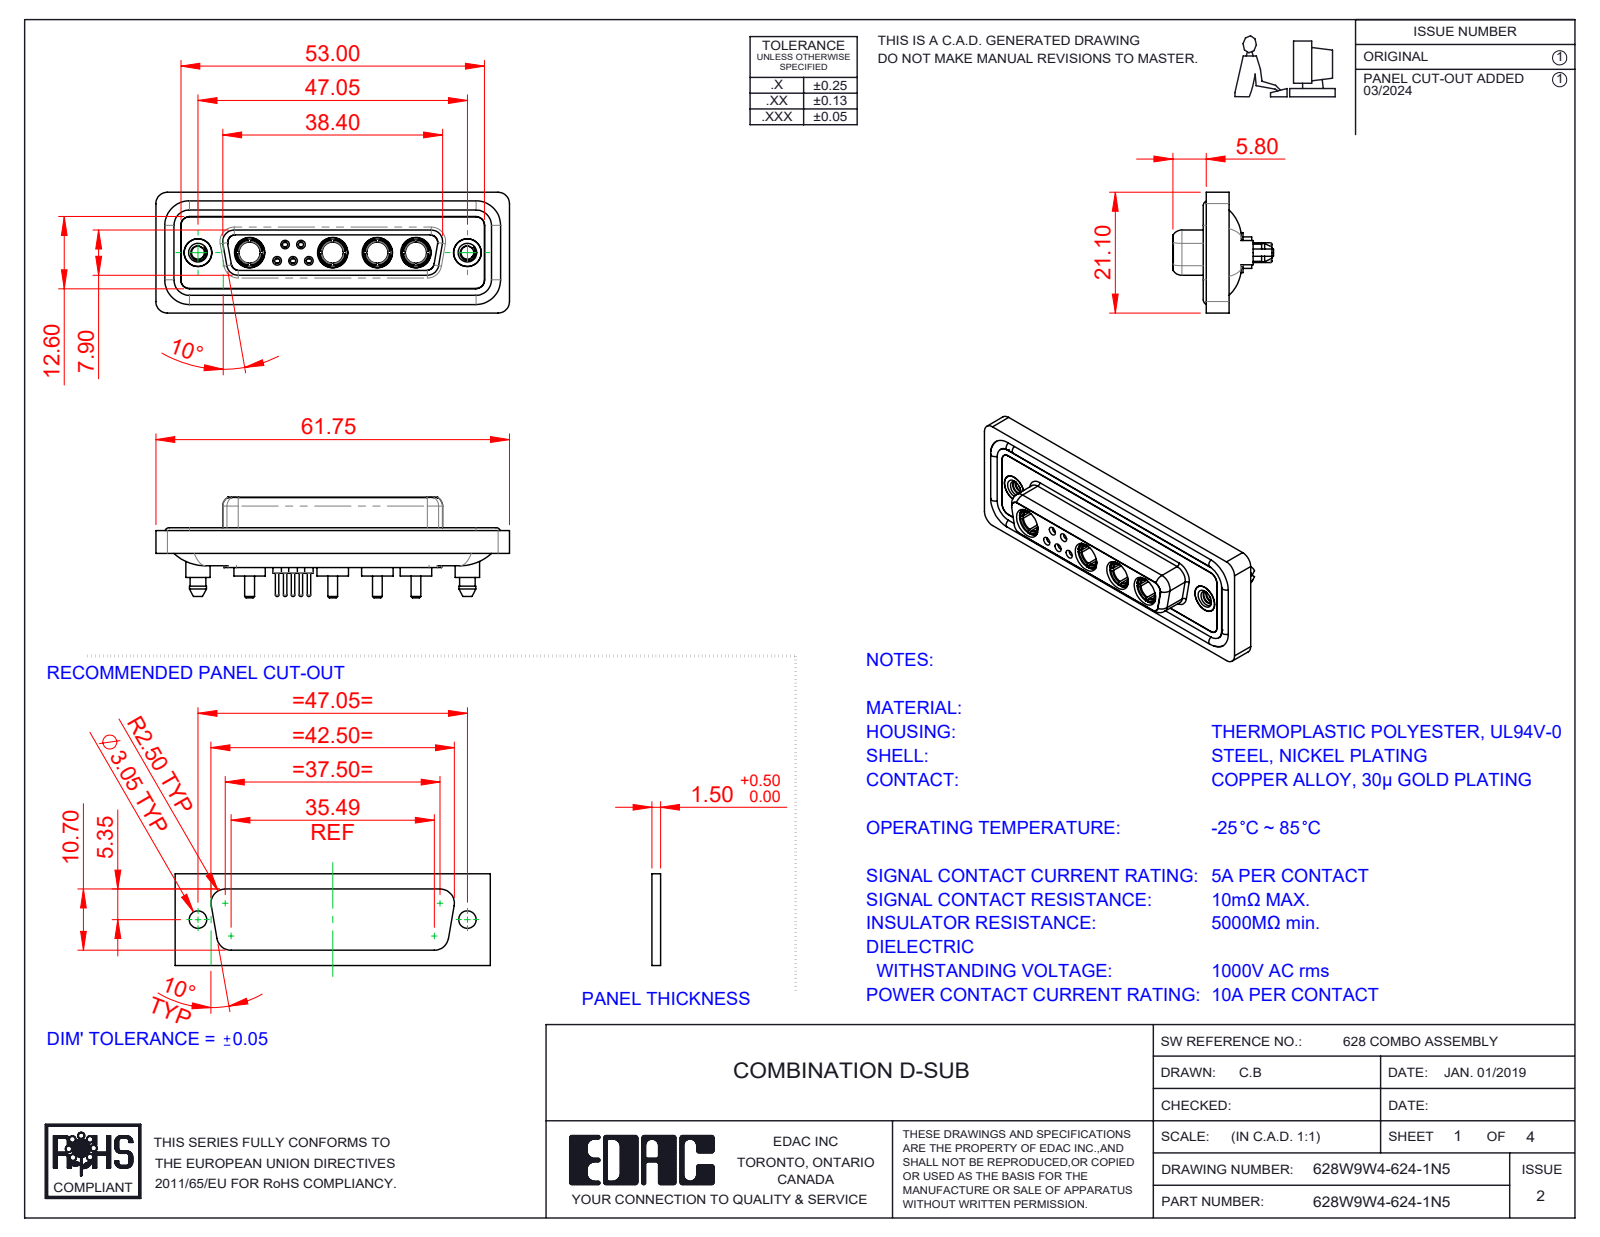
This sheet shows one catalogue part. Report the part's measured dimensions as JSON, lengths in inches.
{"part_name": "628Combo Threaded Boardlock_5; 628W9W4-624-1N5; 628Combo Waterproof Housing_25 Contacts; 628Combo Shell Rear_25 Contacts (+5 more)", "step_written_by": "SolidWorks 2023 (CONFIG_CONTROL_DESIGN)", "units": "inches", "bodies": {"solids": 20, "faces": 1007, "planar": 312, "cylindrical": 407, "other": 288}, "overall_size": [2.431, 0.831, 0.691], "volume_in3": 0.506, "surface_area_in2": 21.46, "round_holes": [[0.191, 6], [0.035, 5], [0.043, 5], [0.059, 5], [0.079, 5], [0.146, 4], [0.209, 4], [0.063, 3], [0.067, 2], [0.089, 2], [0.157, 2], [0.159, 2]], "round_bosses_or_shafts": [[0.063, 6], [0.087, 5], [0.024, 5], [0.217, 4], [0.205, 4], [0.195, 4], [0.187, 4], [0.148, 4]], "partial_cylinders_radius": [[0.059, 24], [0.079, 18], [0.063, 10], [0.053, 8], [0.01, 4], [0.02, 4], [0.024, 4], [0.026, 4]], "face_to_face_distances": [0.016, 0.071, 0.293, 0.222, 0.02, 0.278, 0.26, 0.063, 0.043, 0.114], "hole_center_spacings": [0.124, 0.109, 0.198, 0.109, 0.173, 0.198, 0.218, 0.226]}
